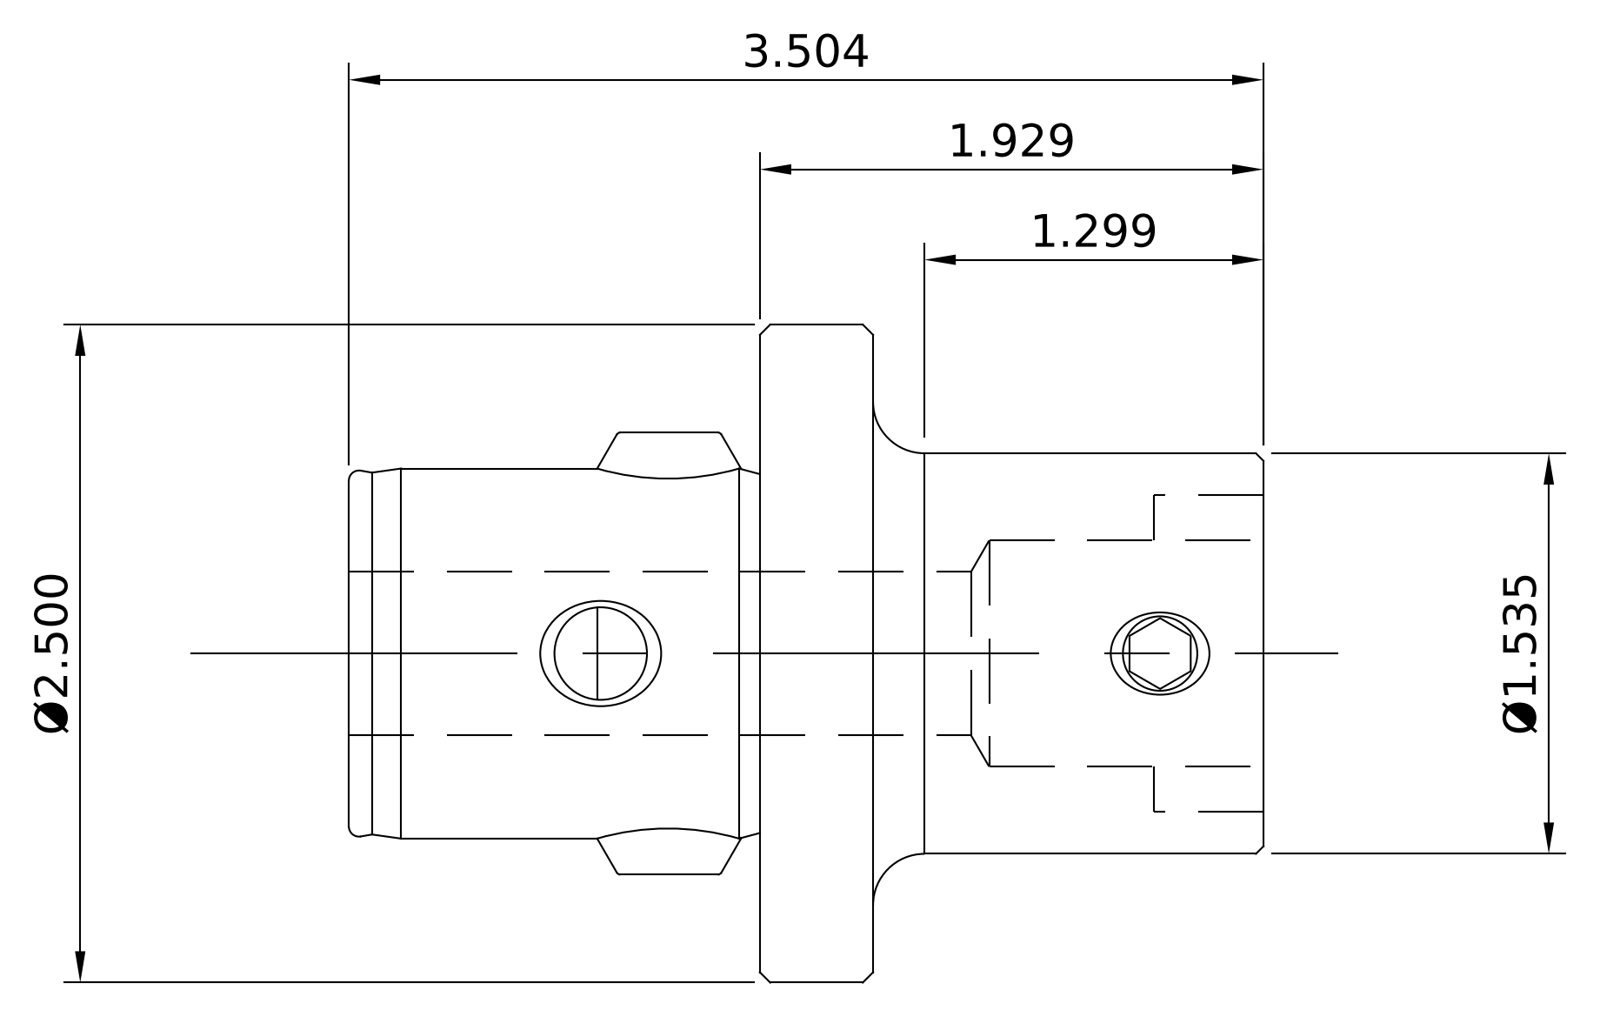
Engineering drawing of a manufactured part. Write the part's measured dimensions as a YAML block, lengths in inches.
part_name: "11.332.641_10.332.640; 10.690.43X_10.690.434; 10.691.50X_10.691.506; 691-50XRing_10.691.506Ring (+1 more)"
step_written_by: "SolidWorks 2015 (AUTOMOTIVE_DESIGN)"
units: inches
bodies: {solids: 4, faces: 146, planar: 41, cylindrical: 49, other: 56}
overall_size: [3.504, 2.491, 2.491]
volume: 6.121
surface_area: 39.55
round_holes:
  - {diameter: 0.197, count: 1}
  - {diameter: 0.268, count: 1}
  - {diameter: 0.323, count: 1}
  - {diameter: 0.354, count: 1}
  - {diameter: 0.551, count: 1}
  - {diameter: 0.63, count: 1}
  - {diameter: 0.728, count: 1}
  - {diameter: 0.866, count: 1}
  - {diameter: 0.886, count: 1}
round_bosses_or_shafts:
  - {diameter: 2.491, count: 1}
  - {diameter: 1.535, count: 1}
  - {diameter: 1.52, count: 1}
  - {diameter: 1.417, count: 1}
  - {diameter: 0.547, count: 1}
  - {diameter: 0.469, count: 1}
  - {diameter: 0.39, count: 1}
  - {diameter: 0.315, count: 1}
partial_cylinders:
  - {radius: 0.138, count: 2}
  - {radius: 0.709, count: 1}
face_to_face_distances: [0.472, 1.457, 1.929, 1.575, 2.047, 3.504, 0.744, 1.693, 0.598, 1.094]
hole_center_spacings: [0.591, 2.144]
